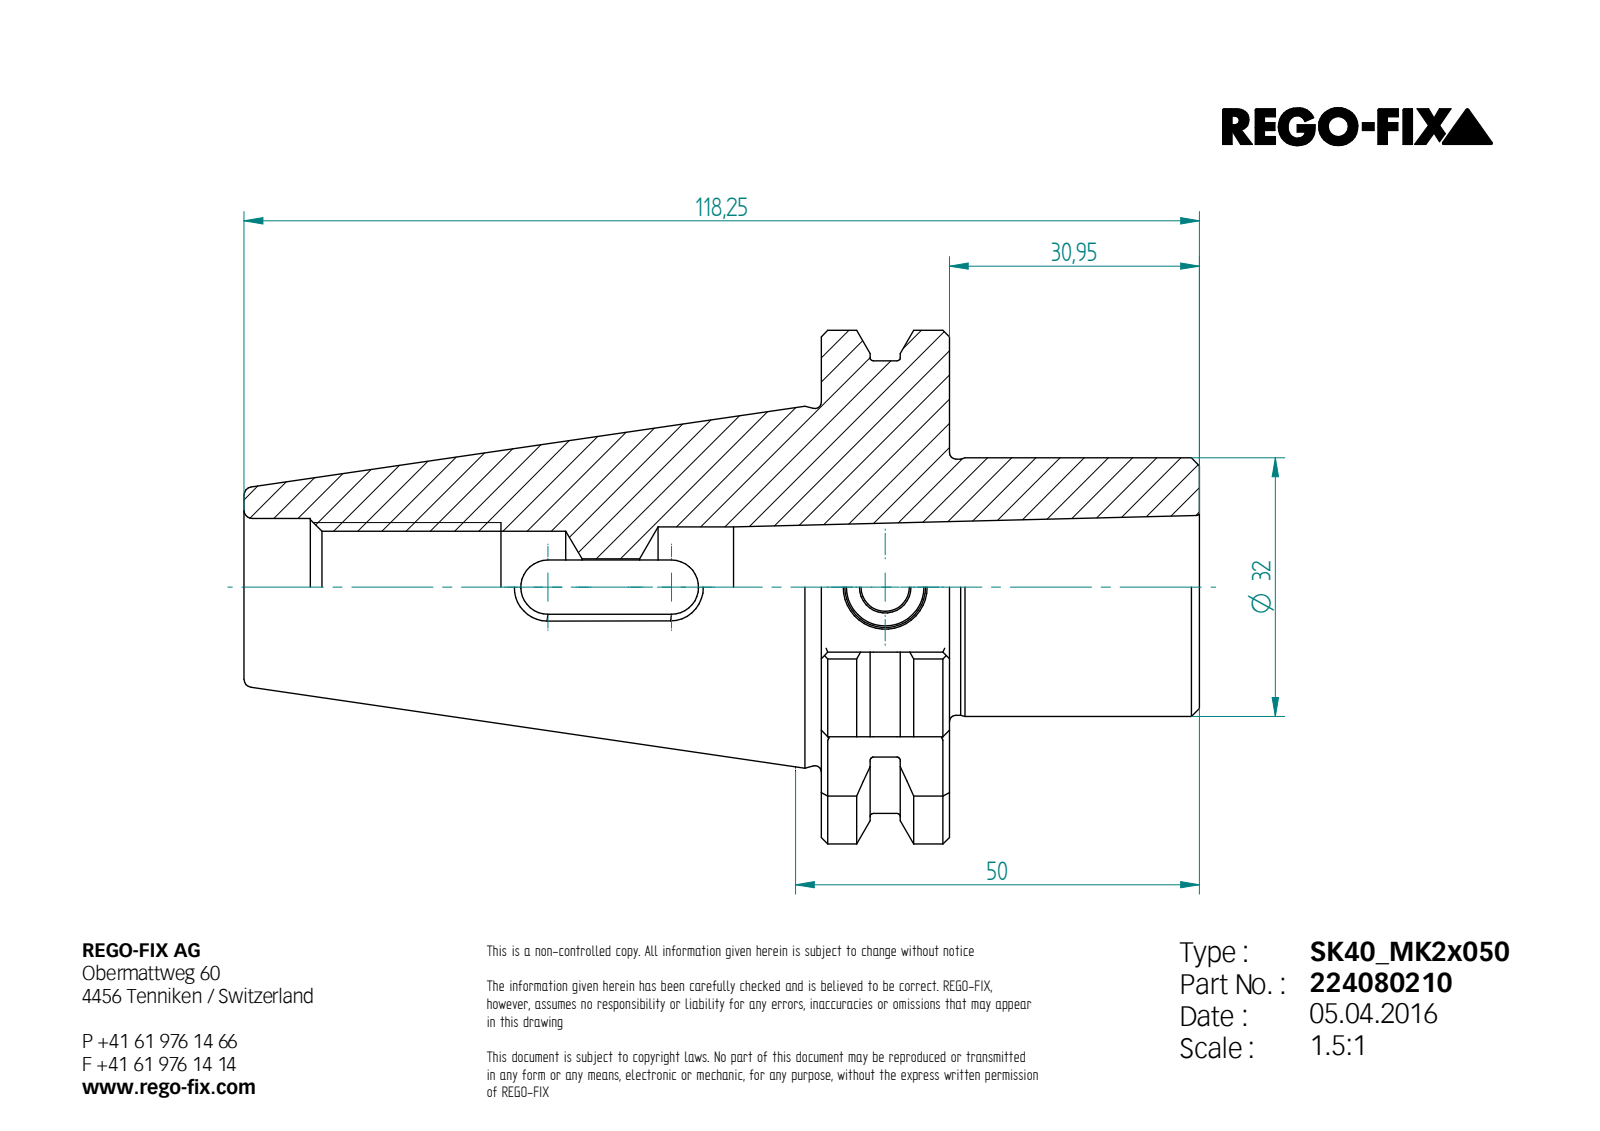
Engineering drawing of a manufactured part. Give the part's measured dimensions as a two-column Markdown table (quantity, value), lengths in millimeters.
| quantity | value |
| --- | --- |
| STEP written by | Unknown (AUTOMOTIVE_DESIGN) |
| units | millimeters |
| bodies | 1 solid, 125 faces (44 planar, 36 cylindrical, 45 other) |
| overall size | 118.25 × 63.55 × 61.01 |
| volume | 112 861 mm³ |
| surface area | 25 673 mm² |
| round holes (diameter × count) | 6 × 1, 10 × 1, 13.84 × 1, 14.9 × 1, 17 × 1 |
| round bosses / shafts (diameter × count) | 32 × 1, 31.7 × 1 |
| partial cylindrical surfaces (radius × count) | 0.5 × 13, 3.35 × 2, 3.5 × 1, 28 × 1, 31.77 × 1 |
| main face-to-face distances | 15.85, 46.8, 30.95, 6.7, 4.7, 11.4, 47.3, 16.1, 71.45, 87.3 |
